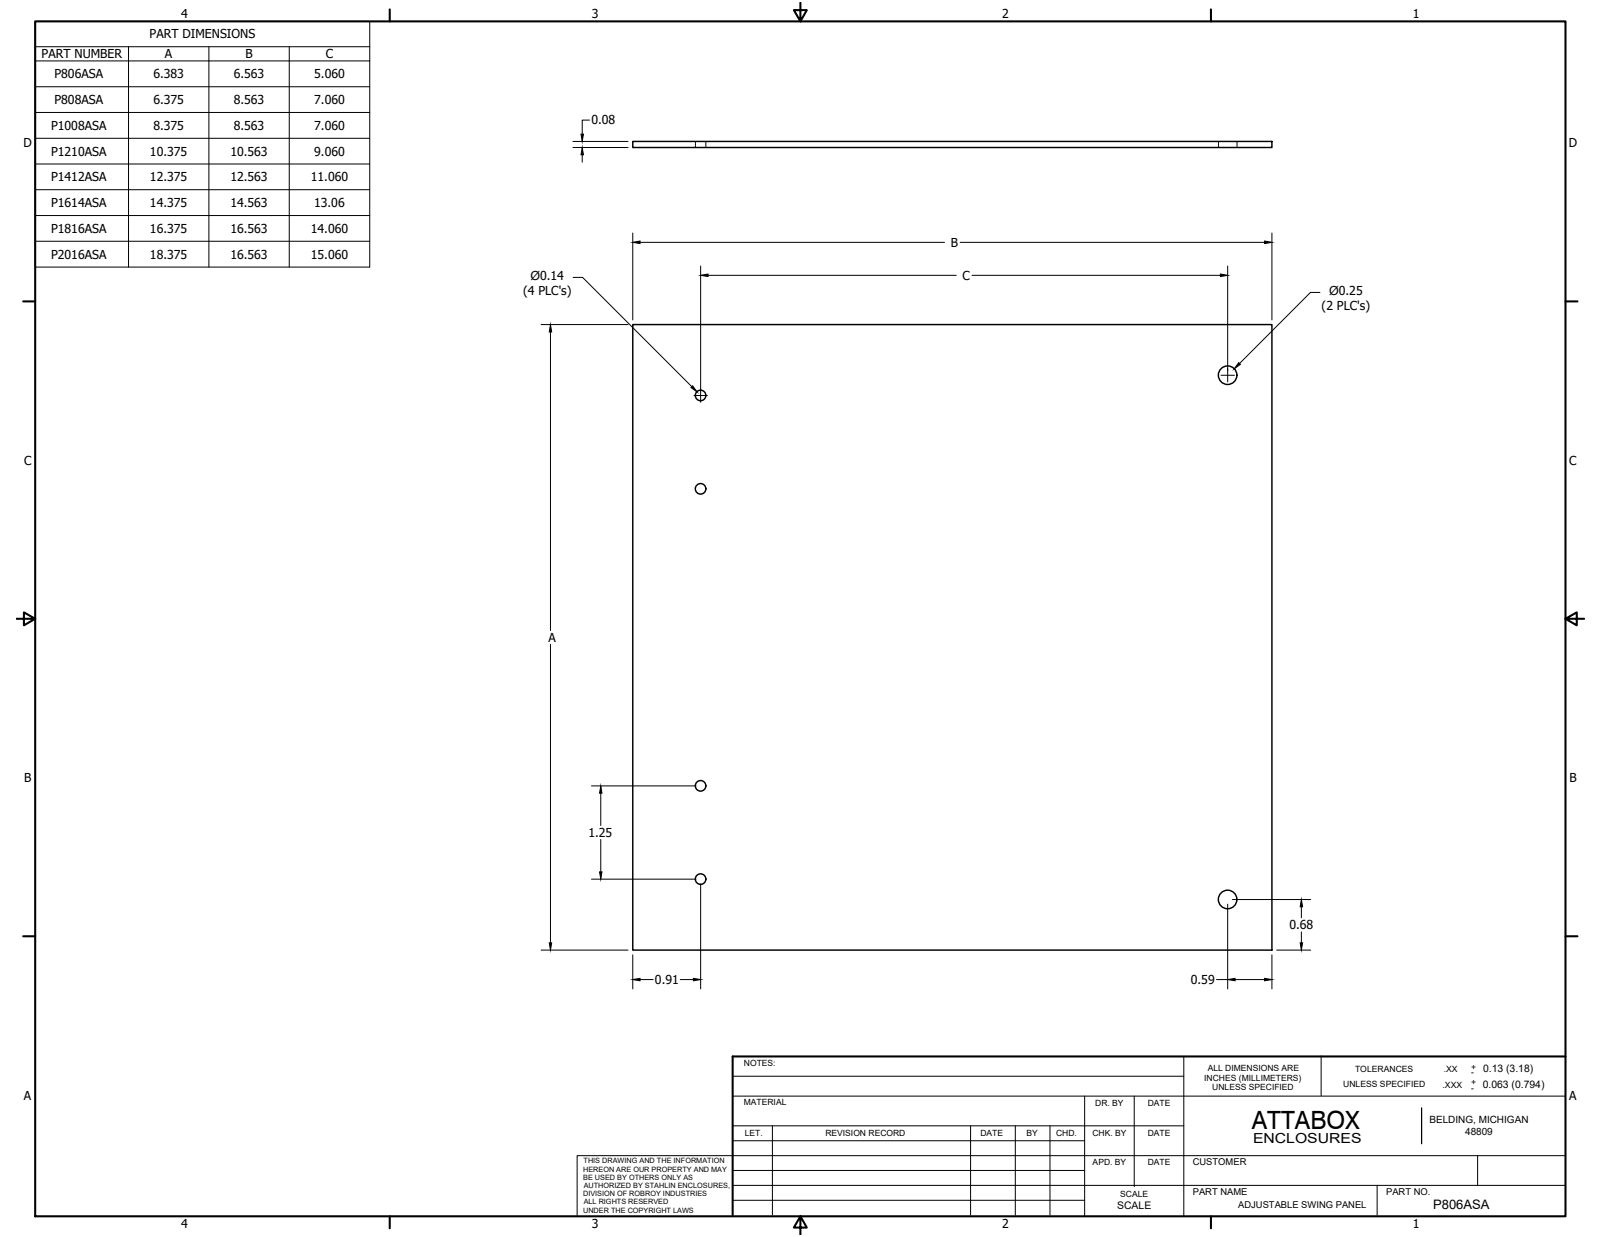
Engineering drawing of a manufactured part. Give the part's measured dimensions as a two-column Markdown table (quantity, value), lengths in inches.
| quantity | value |
| --- | --- |
| part name | P806ASAL |
| STEP written by | Autodesk Inventor 11 (AUTOMOTIVE_DESIGN) |
| units | inches |
| bodies | 1 solid, 12 faces (6 planar, 6 cylindrical, 0 other) |
| overall size | 6.563 × 6.383 × 0.08 |
| volume | 3.338 in³ |
| surface area | 85.79 in² |
| round holes (diameter × count) | 0.14 × 4, 0.25 × 2 |
| main face-to-face distances | 0.08, 6.383, 6.562 |
| hole center spacings | 1.25, 3.226, 5.068, 5.284, 6.151, 6.939, 1.976, 4.476 |
